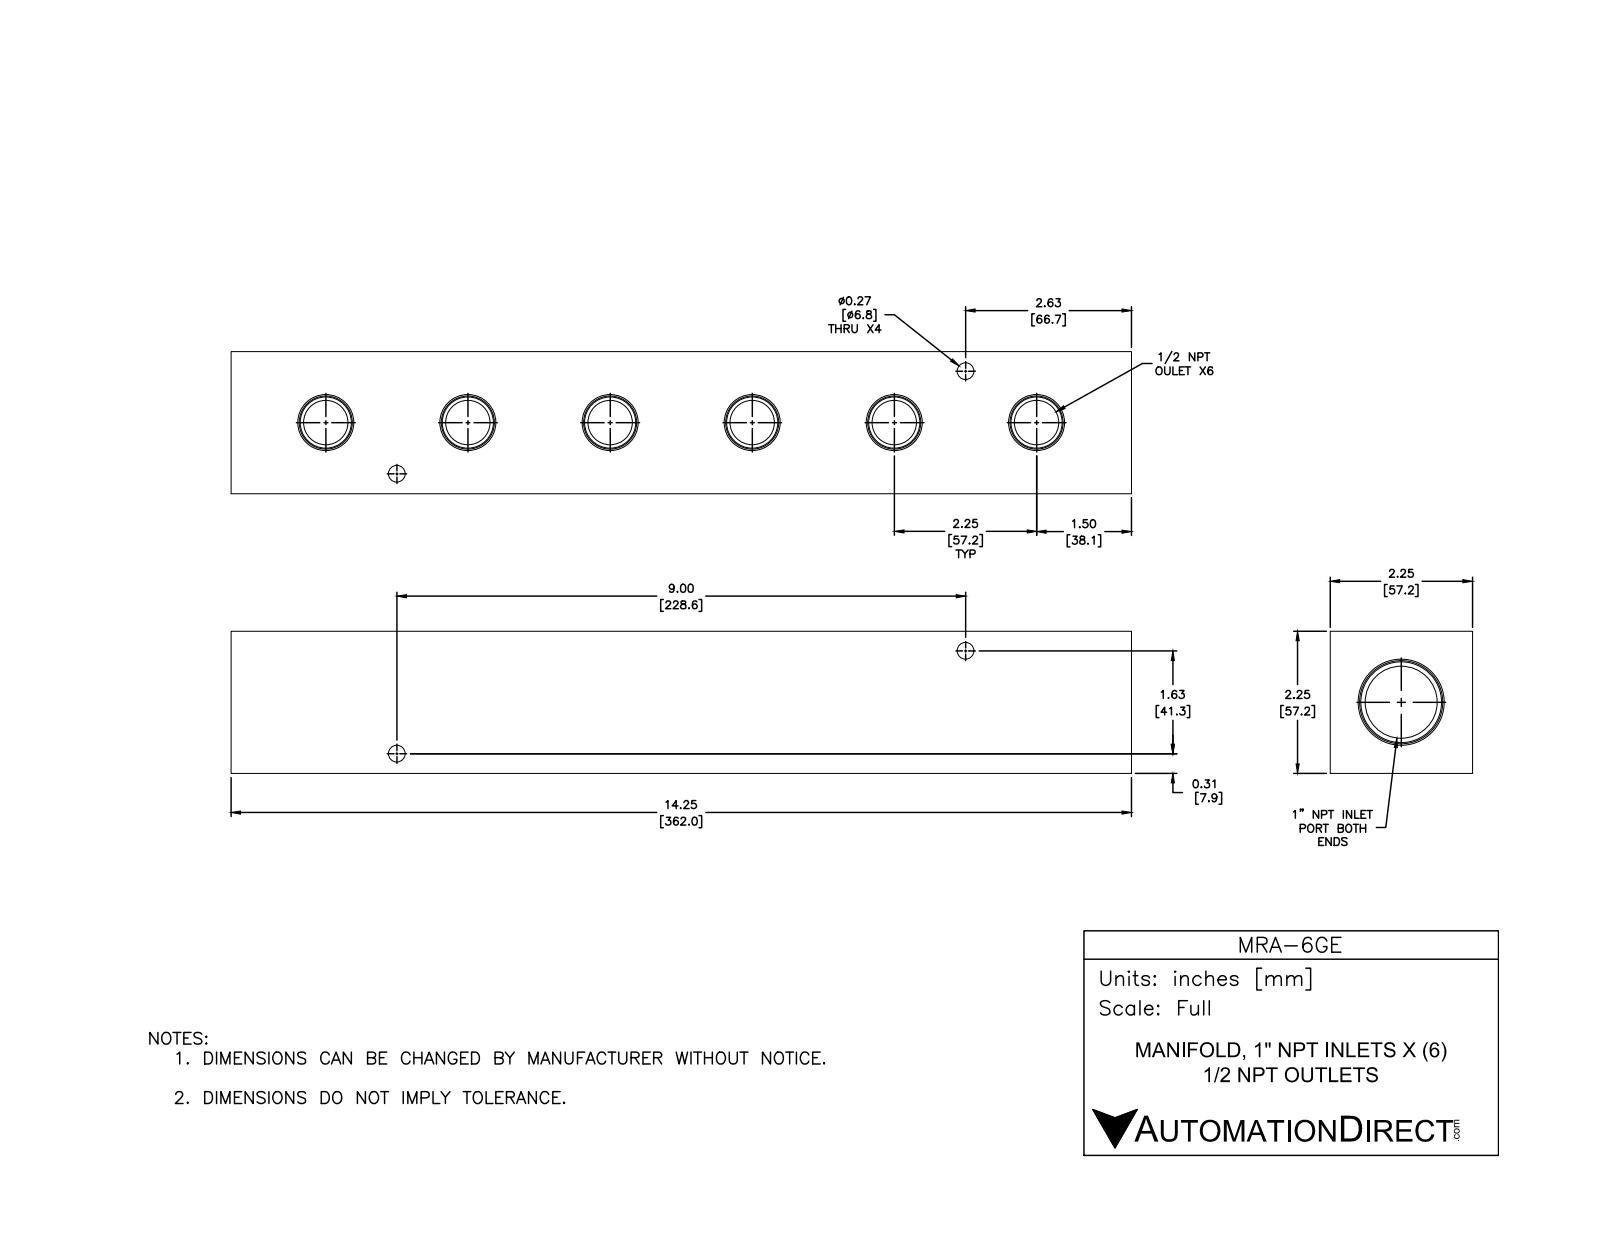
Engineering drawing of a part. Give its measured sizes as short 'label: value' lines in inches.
name: MRA-6GE
written by: SolidWorks 2015 (CONFIG_CONTROL_DESIGN)
unit: in
bodies: 1 solid, 76 faces (14 planar, 30 cylindrical, 32 other)
size: 14.25 × 2.25 × 2.25
volume: 54.87 in³; area: 198.4 in²
holes: 6× ⌀0.703, 4× ⌀0.266, 1× ⌀1.141
face distances: 2.25, 14.25, 1.72, 0.53, 0.66, 13.59, 12.93
hole spacings: 1.388, 2.25, 2.25, 4.5, 7.917, 9, 9.146, 10.158
